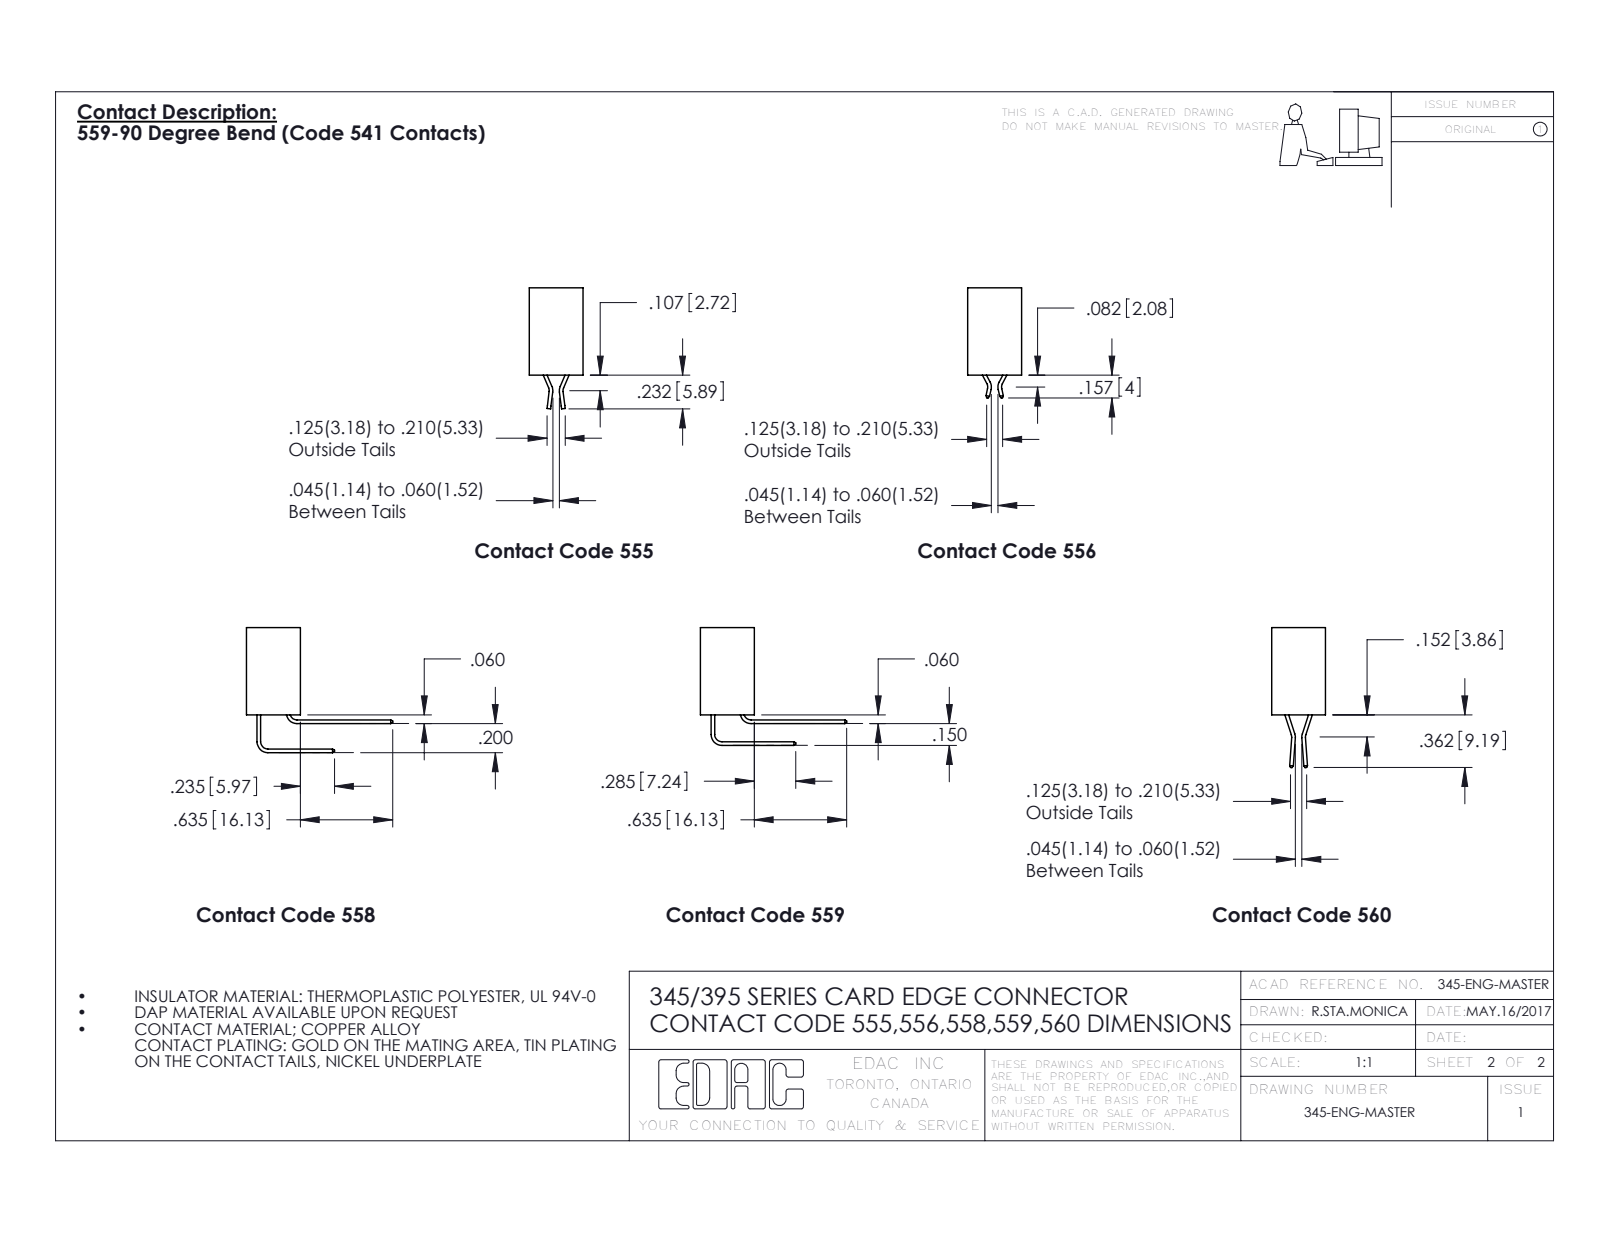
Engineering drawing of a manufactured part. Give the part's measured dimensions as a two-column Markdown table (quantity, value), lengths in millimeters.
| quantity | value |
| --- | --- |
| part name | 395-104-560-212; 345-292-001_560 Tail; 345 Part_Flush Mounting Lugs - Side Mount |
| STEP written by | SolidWorks 2016 (CONFIG_CONTROL_DESIGN) |
| units | millimeters |
| bodies | 105 solids, 5534 faces (3512 planar, 2022 cylindrical, 0 other) |
| overall size | 153.3 × 24.4 × 9.4 |
| volume | 15 600 mm³ |
| surface area | 24 840 mm² |
| round holes (diameter × count) | 3.3 × 2, 1.6 × 1 |
| partial cylindrical surfaces (radius × count) | 0.2 × 156, 0.3 × 22, 0.2 × 6, 0.8 × 6, 0.7 × 3, 0.3 × 2, 0.4 × 2, 0.5 × 2 |
| main face-to-face distances | 0.6, 7.6, 1.8, 5.1, 9.4, 2.5, 6.9, 5.7, 4.4, 3.8 |
| hole center spacings | 146.7 |
